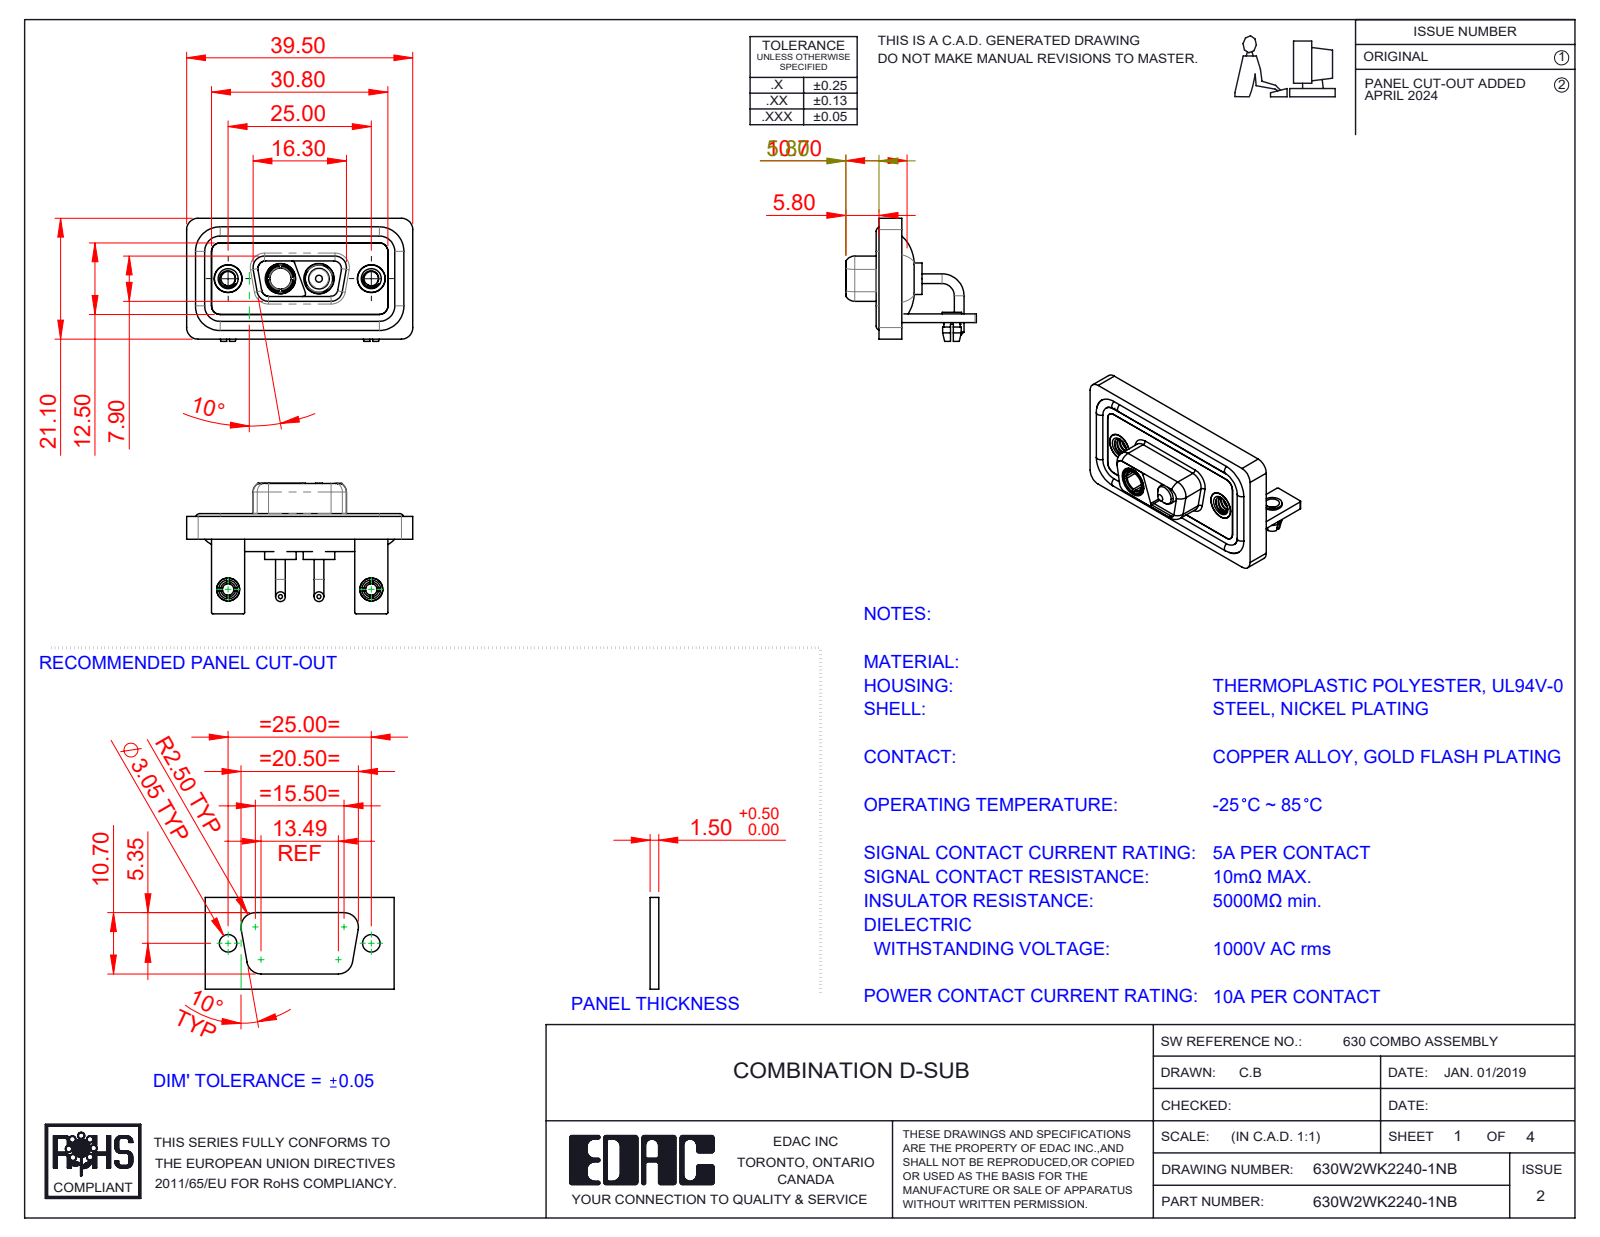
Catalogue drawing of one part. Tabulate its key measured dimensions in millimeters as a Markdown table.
| quantity | value |
| --- | --- |
| part name | 630W2WK2140-1NB; 630Combo Shell Front_09 Contacts; 630Combo Stabilizer Bracket_50 Contacts; Power Pin_10A RA (+6 more) |
| STEP written by | SolidWorks 2023 (CONFIG_CONTROL_DESIGN) |
| units | millimeters |
| bodies | 15 solids, 642 faces (212 planar, 289 cylindrical, 141 other) |
| overall size | 39.5 × 22.8 × 21.5 |
| volume | 4 986 mm³ |
| surface area | 8 342 mm² |
| round holes (diameter × count) | 2.5 × 4, 4.85 × 4, 2 × 2, 3.2 × 2, 4 × 2, 4.05 × 2, 5 × 2, 5.3 × 2, 3.7 × 1 |
| round bosses / shafts (diameter × count) | 1.7 × 4, 1.6 × 4, 5.5 × 2, 5.2 × 2, 4.95 × 2, 4.8 × 2, 4.75 × 2, 4 × 2 |
| partial cylindrical surfaces (radius × count) | 2 × 19, 1.5 × 18, 0.25 × 16, 1.35 × 8, 1.6 × 8, 0.5 × 7, 0.6 × 4, 0.65 × 4 |
| main face-to-face distances | 0.4, 2.9, 1.5, 1.1, 3.7, 1.8, 0.8, 2.5, 1.6, 3.1 |
| hole center spacings | 9.14, 15.86, 25, 6.72 |
